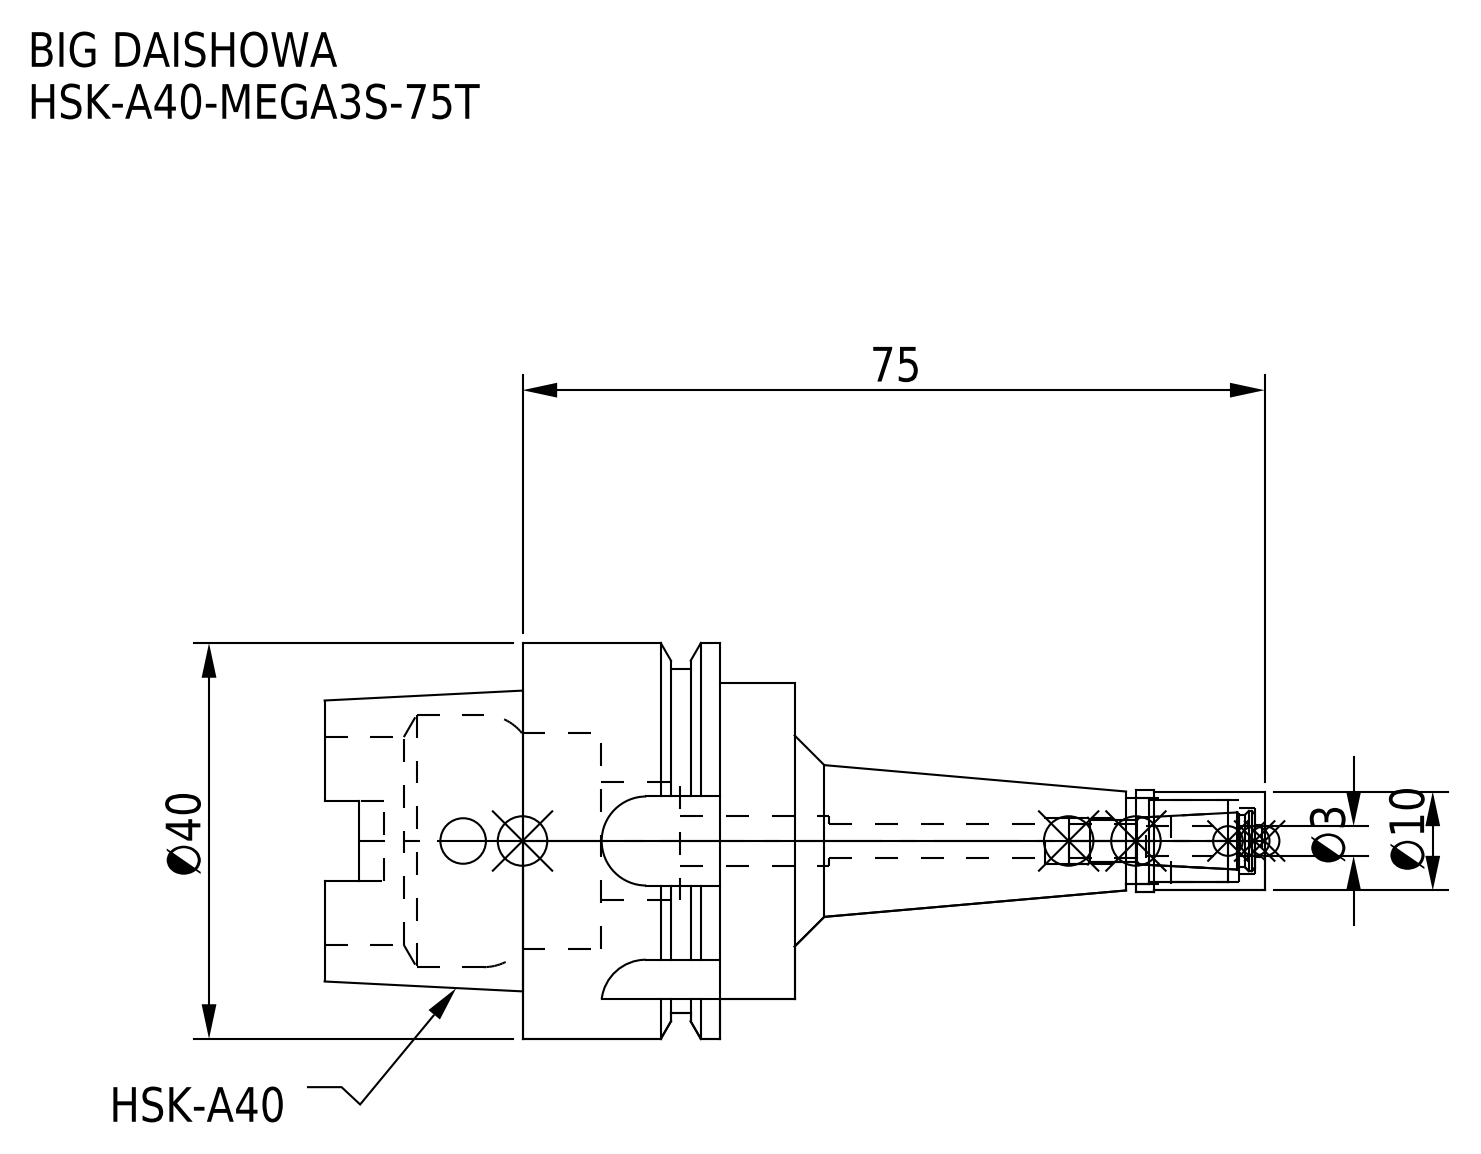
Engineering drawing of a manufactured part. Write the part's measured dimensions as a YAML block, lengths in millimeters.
part_name: "MGN3S_1.stp; HSK-A40-MEGA3S-75T_2.stp; HA40MS03075T-030_ASM.stp; HSK-A40-MEGA3S-75T (+3 more)"
step_written_by: "SolidWorks 2019 (CONFIG_CONTROL_DESIGN)"
units: millimeters
bodies: {solids: 2, faces: 123, planar: 47, cylindrical: 54, other: 22}
overall_size: [95, 40, 40]
volume: 35274
surface_area: 13326
round_holes:
  - {diameter: 3.3, count: 1}
  - {diameter: 3.4, count: 1}
  - {diameter: 4.6, count: 1}
  - {diameter: 4.7, count: 1}
  - {diameter: 5, count: 1}
  - {diameter: 6.6, count: 1}
  - {diameter: 8.2, count: 1}
  - {diameter: 8.7, count: 1}
  - {diameter: 12, count: 1}
  - {diameter: 21, count: 1}
  - {diameter: 21.8, count: 1}
  - {diameter: 25.5, count: 1}
round_bosses_or_shafts:
  - {diameter: 40, count: 1}
  - {diameter: 34.8, count: 1}
  - {diameter: 32, count: 1}
  - {diameter: 10.3, count: 1}
  - {diameter: 10, count: 1}
partial_cylinders:
  - {radius: 1.88, count: 4}
  - {radius: 4.5, count: 4}
face_to_face_distances: [20, 27.5, 7.5, 19.55, 12.05, 7.95, 47.5, 40, 27.95, 34]
